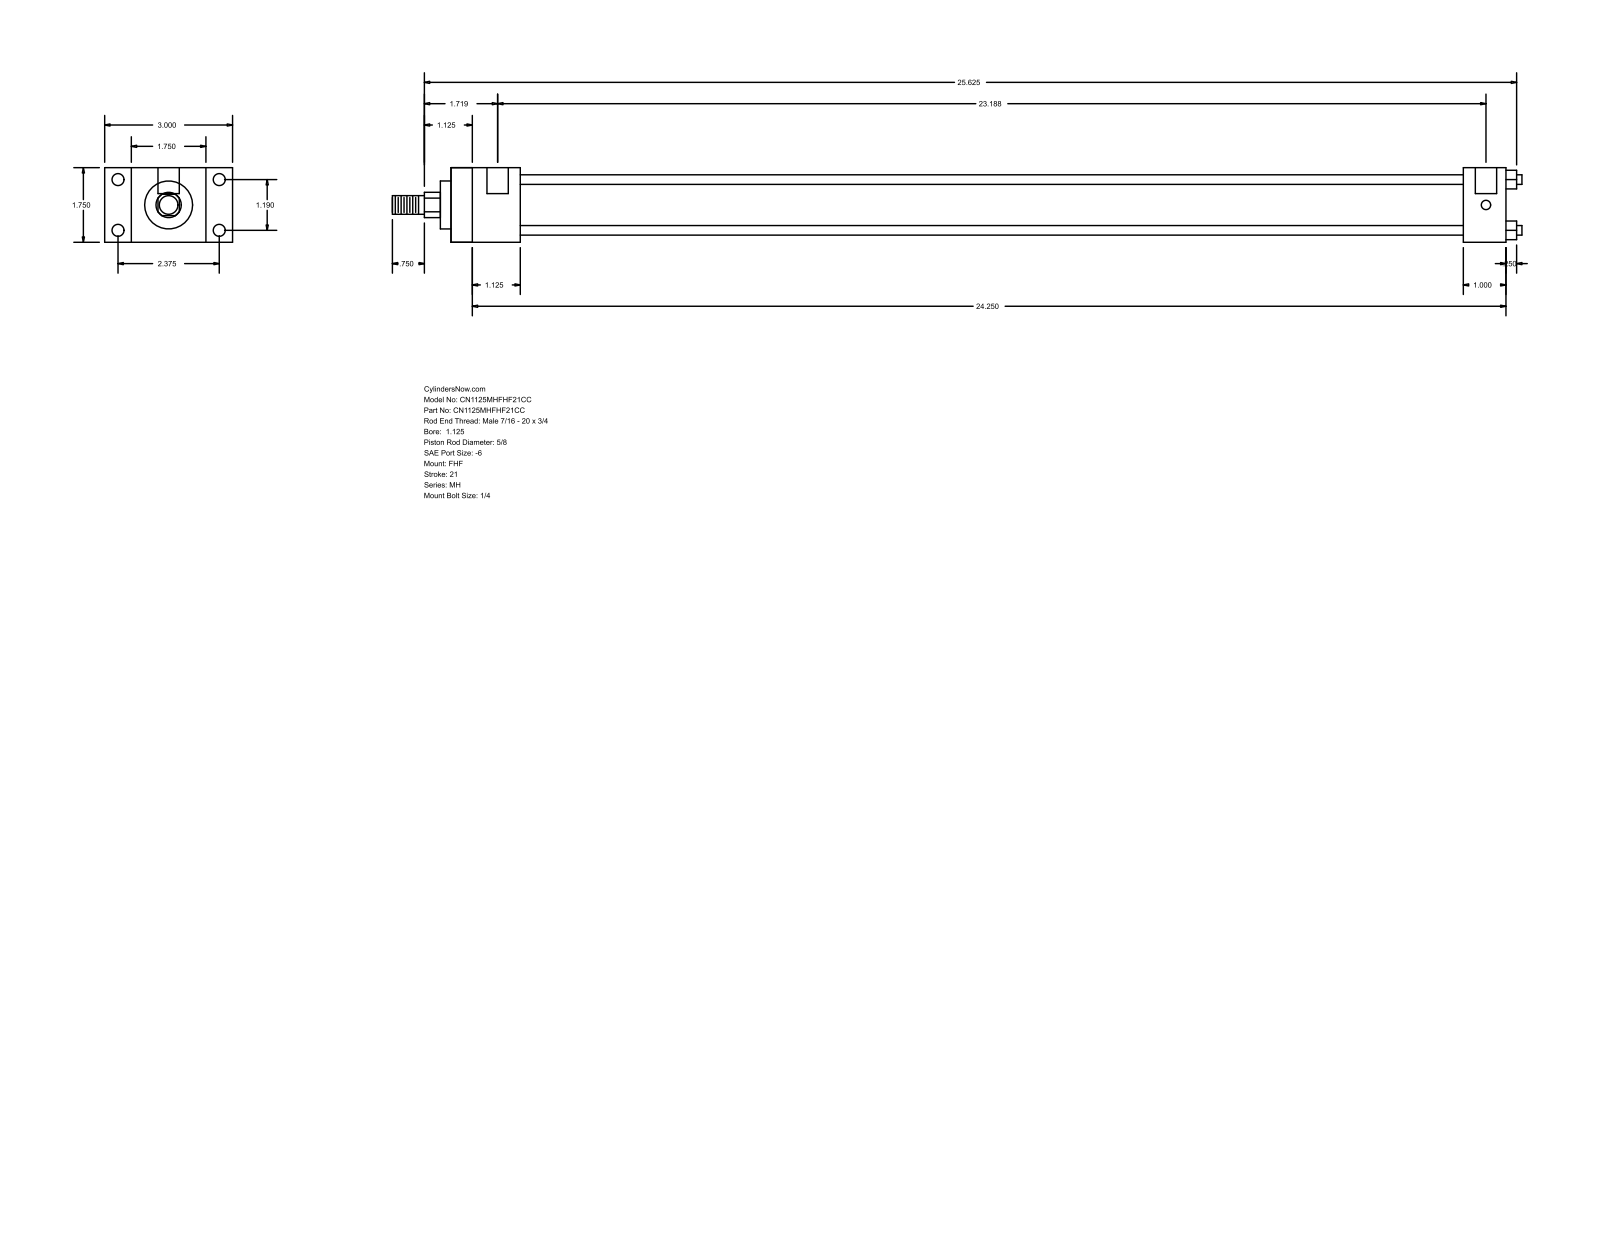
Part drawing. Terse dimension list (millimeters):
name: MH_FHF__0112_0.625
written by: GSSL Pune (CONFIG_CONTROL_DESIGN)
unit: mm
bodies: 0 solids, 88 faces (60 planar, 28 cylindrical, 0 other)
size: 673.1 × 76.2 × 44.45
holes: 4× ⌀5.56, 4× ⌀7.14, 2× ⌀12.7
bosses: 4× ⌀5.71, 1× ⌀34.92, 1× ⌀28.57, 1× ⌀15.88, 1× ⌀11.11
rounds: 1× R7.54
face distances: 44.46, 15.87, 60.33, 41.27, 76.2, 628.64, 587.37, 25.4, 603.24, 561.97
hole spacings: 30.22, 60.32, 67.47, 585.79, 3.17, 588.96
